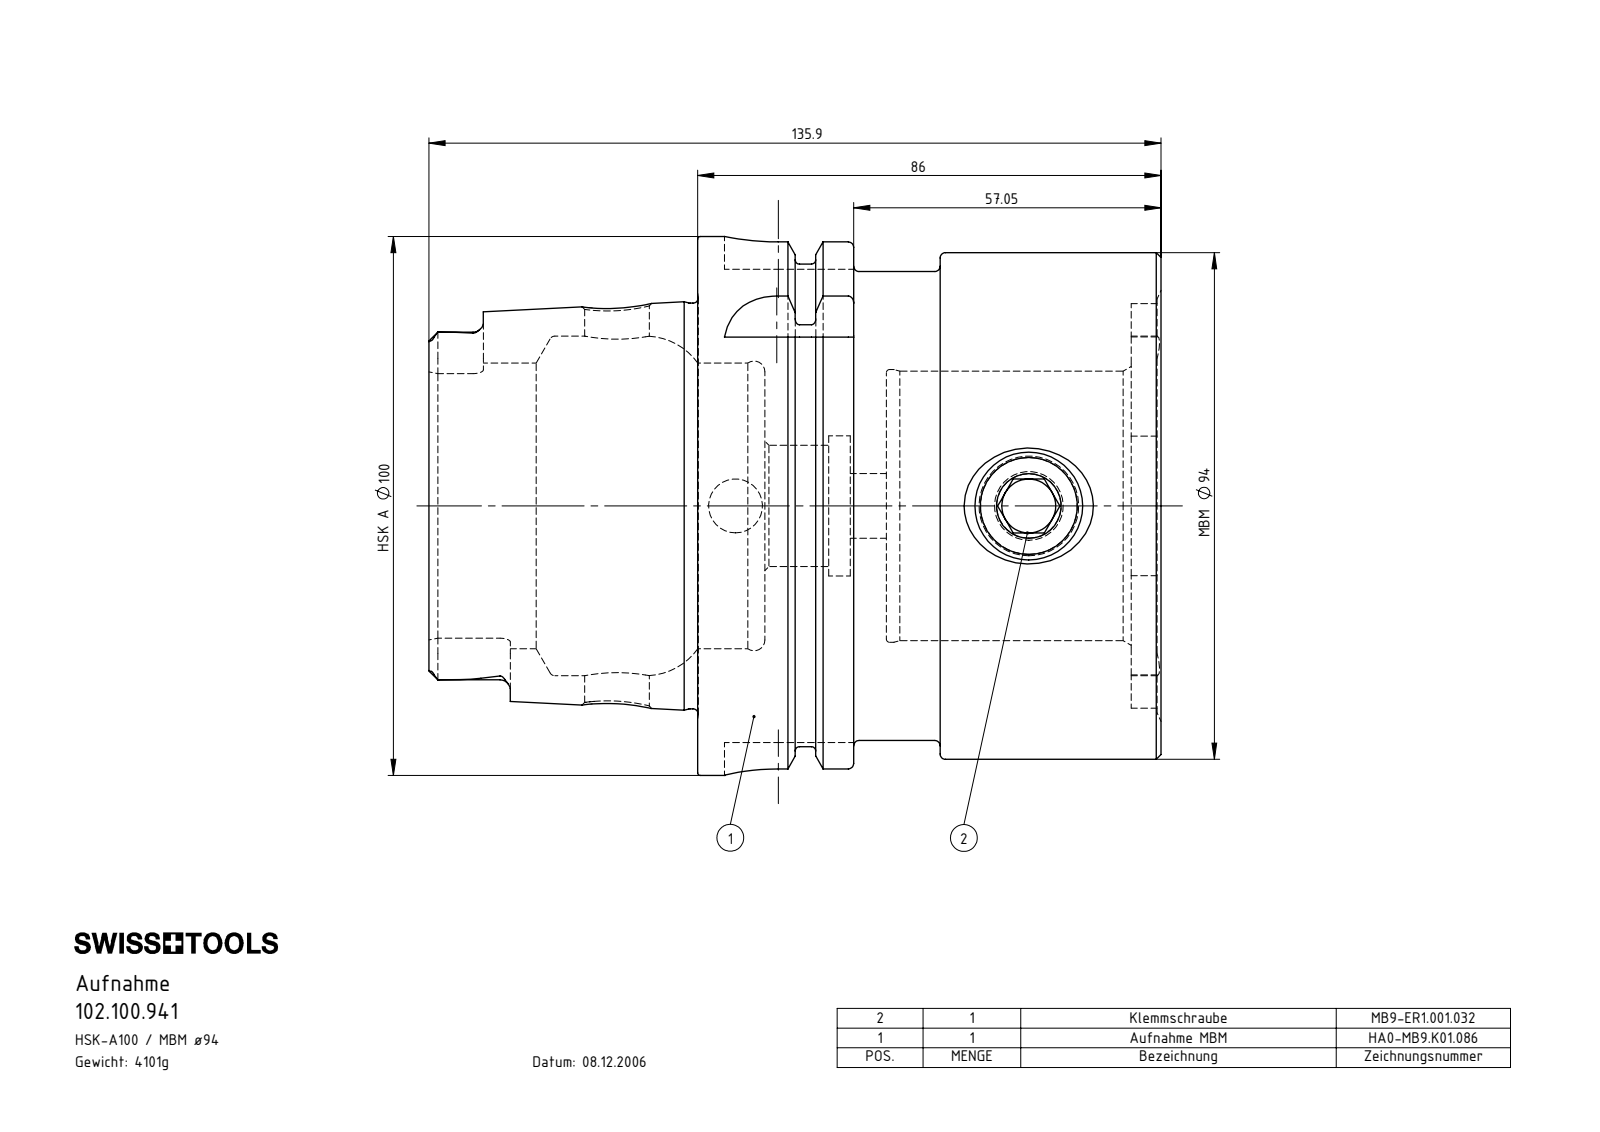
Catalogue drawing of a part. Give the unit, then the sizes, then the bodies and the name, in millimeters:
Units: millimetres
Overall size (bounding box): 135.9 × 100 × 100
Round holes (diameter × count): ⌀10 ×2, ⌀12 ×2, ⌀18.5 ×1, ⌀22.5 ×1, ⌀26 ×1, ⌀50 ×1, ⌀50.6 ×1, ⌀53 ×1, ⌀63 ×1
Round bosses / shafts (diameter × count): ⌀100 ×1, ⌀94 ×1, ⌀91.95 ×1, ⌀87 ×1, ⌀75.26 ×1, ⌀20 ×1
Partial cylindrical surfaces — rounded edges, fillets, slot ends (radius × count): R1.9 ×6, R4.88 ×4, R5.2 ×4, R10 ×4, R30 ×1, R37.52 ×1
Main face-to-face distances: 35, 80.45, 45.45, 86, 51, 5.55, 12.45, 22.55, 68, 73.55
Hole centre spacings: 54.45
Volume: 522 302 mm³ · Surface area: 79 201 mm²
Bodies: 2 solids, 173 faces (70 planar, 46 cylindrical, 57 other)
Part name (STEP PRODUCT): MB9-ER1.001.032_A; HA0.MB9.K01.086; HA0-MB9.K01.086_B_Fertigbearbeitung
STEP written by: SolidWorks 2017 (AUTOMOTIVE_DESIGN)
